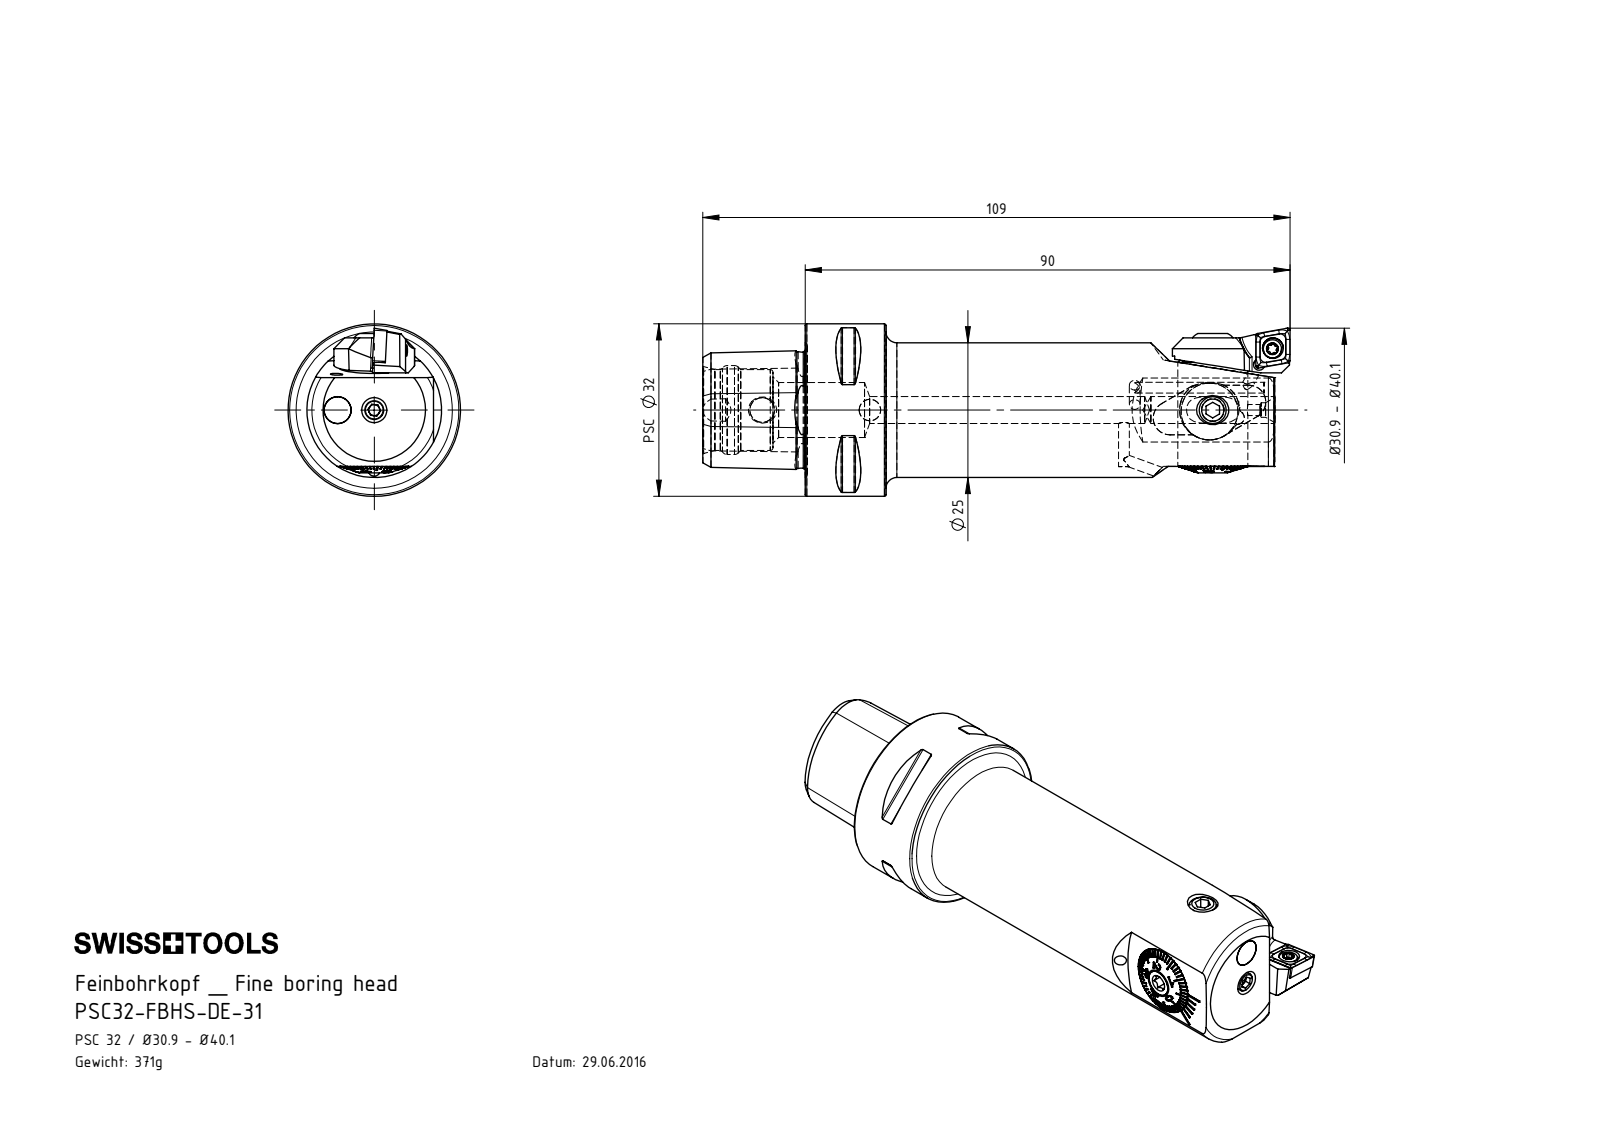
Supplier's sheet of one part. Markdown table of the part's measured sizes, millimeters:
| quantity | value |
| --- | --- |
| part name | F25-BG2.010.011_A; F25-BG3.005.018_A_Abgedreht; PS3-F25.DA1.090_A; F25-ER1.101.008_A (+8 more) |
| STEP written by | SolidWorks 2017 (AUTOMOTIVE_DESIGN) |
| units | millimeters |
| bodies | 15 solids, 672 faces (362 planar, 99 cylindrical, 211 other) |
| overall size | 106.15 × 32 × 32 |
| volume | 46 548 mm³ |
| surface area | 17 194 mm² |
| round holes (diameter × count) | 2 × 4, 2.05 × 2, 4.2 × 2, 5 × 2, 0.7 × 1, 2.4 × 1, 2.7 × 1, 3 × 1, 4 × 1, 4.6 × 1, 5.5 × 1, 6.4 × 1 |
| round bosses / shafts (diameter × count) | 1.9 × 6, 5 × 2, 4.95 × 2, 32 × 1, 25 × 1, 13 × 1, 12.98 × 1, 12.85 × 1 |
| partial cylindrical surfaces (radius × count) | 0.3 × 8, 1.1 × 3, 1.2 × 3, 0.5 × 2, 1.32 × 2, 1.4 × 2, 3.1 × 2, 4.8 × 2 |
| main face-to-face distances | 87.15, 1.5, 0.8, 2.35, 72.15, 15, 3.8, 2.3, 12.01, 19 |
| hole center spacings | 2.6, 0.68, 4.48, 6.8, 9.46, 16.5, 20, 63.03 |
